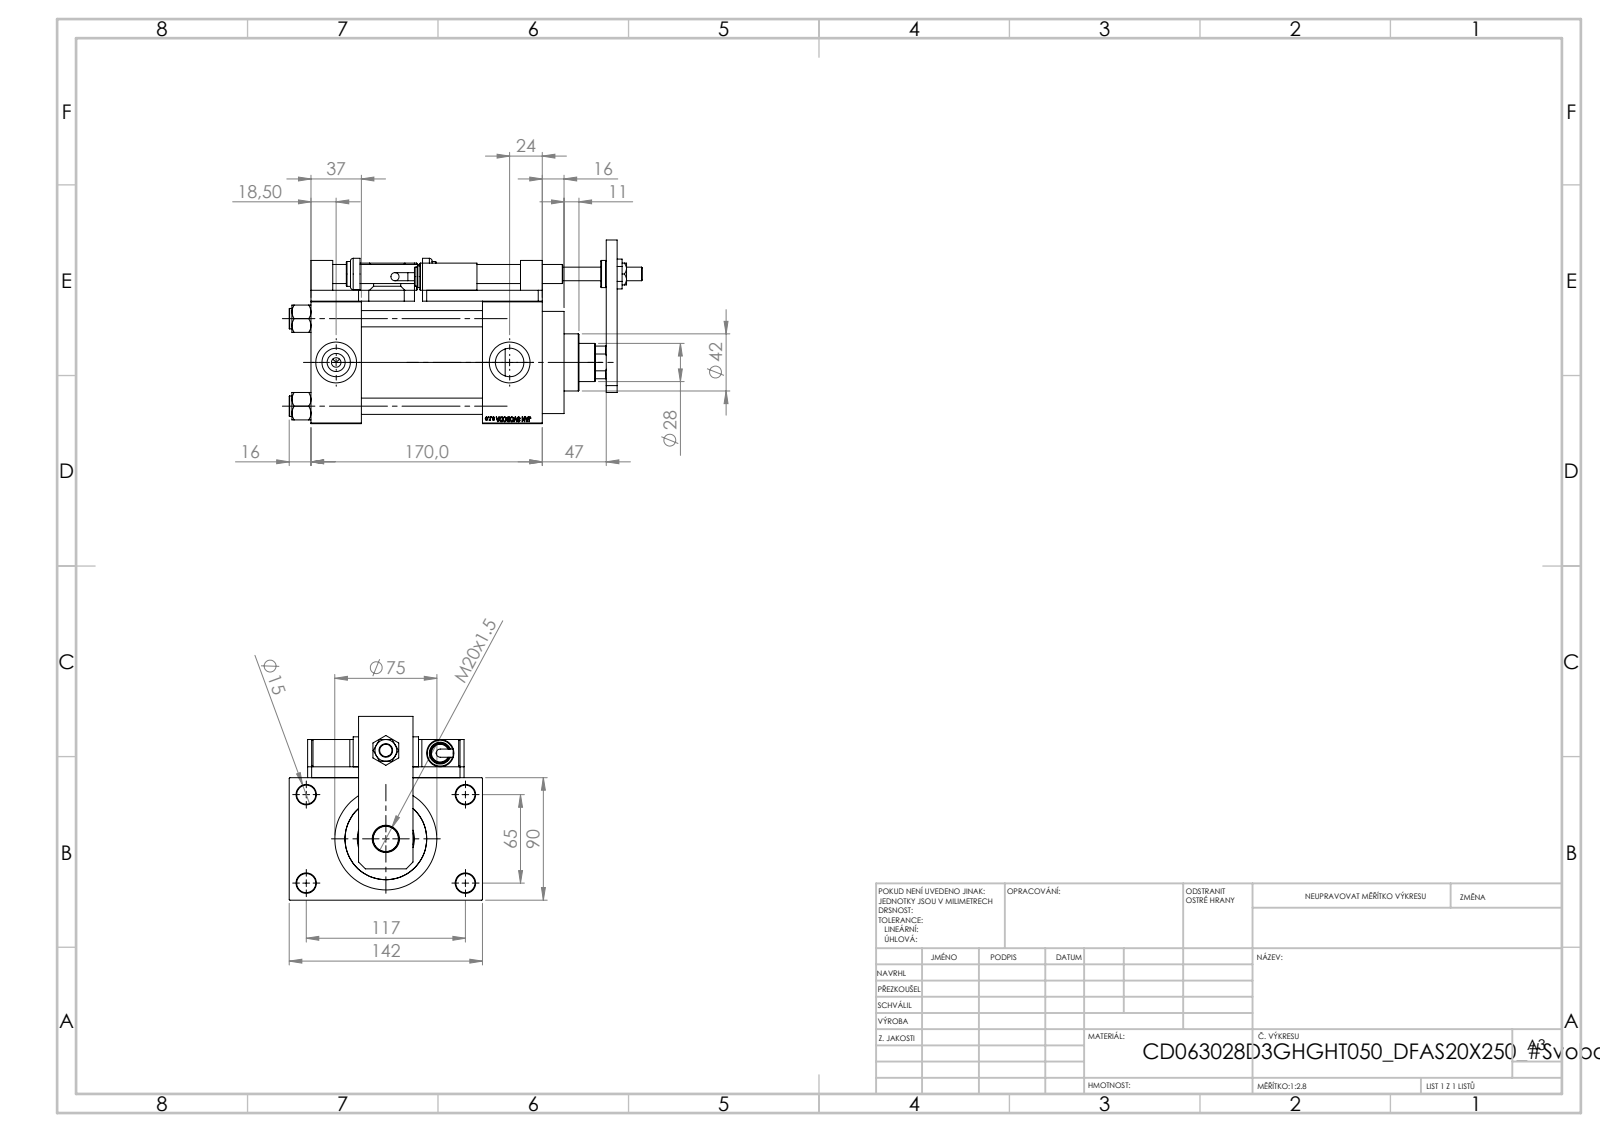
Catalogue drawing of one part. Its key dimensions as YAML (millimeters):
part_name: "V215CD_SWITCH_Q_DIMA; V215CD_SWITCH_Q_NUT10; V215CD_SWITCH_Q_NUT; V215CD_VC_A (+7 more)"
step_written_by: "SolidWorks 2019 (CONFIG_CONTROL_DESIGN)"
units: millimeters
bodies: {solids: 26, faces: 1432, planar: 666, cylindrical: 167, other: 599}
overall_size: [259.5, 142, 135]
volume: 1411000
surface_area: 311105
round_holes:
  - {diameter: 14, count: 5}
  - {diameter: 8.5, count: 4}
  - {diameter: 12, count: 4}
  - {diameter: 13.5, count: 4}
  - {diameter: 20.96, count: 4}
  - {diameter: 30, count: 4}
  - {diameter: 7, count: 3}
  - {diameter: 10, count: 1}
  - {diameter: 18.5, count: 1}
  - {diameter: 20, count: 1}
  - {diameter: 28, count: 1}
  - {diameter: 31, count: 1}
round_bosses_or_shafts:
  - {diameter: 15, count: 4}
  - {diameter: 20, count: 3}
  - {diameter: 16, count: 2}
  - {diameter: 14, count: 2}
  - {diameter: 6, count: 2}
  - {diameter: 75, count: 1}
  - {diameter: 69, count: 1}
  - {diameter: 42, count: 1}
partial_cylinders:
  - {radius: 7.5, count: 4}
  - {radius: 13.5, count: 1}
face_to_face_distances: [8, 90, 44, 170, 37, 98, 133, 126, 89, 47]
hole_center_spacings: [66.92, 26.35, 45.47, 64.3, 69.81, 90.65, 111.34, 65]
